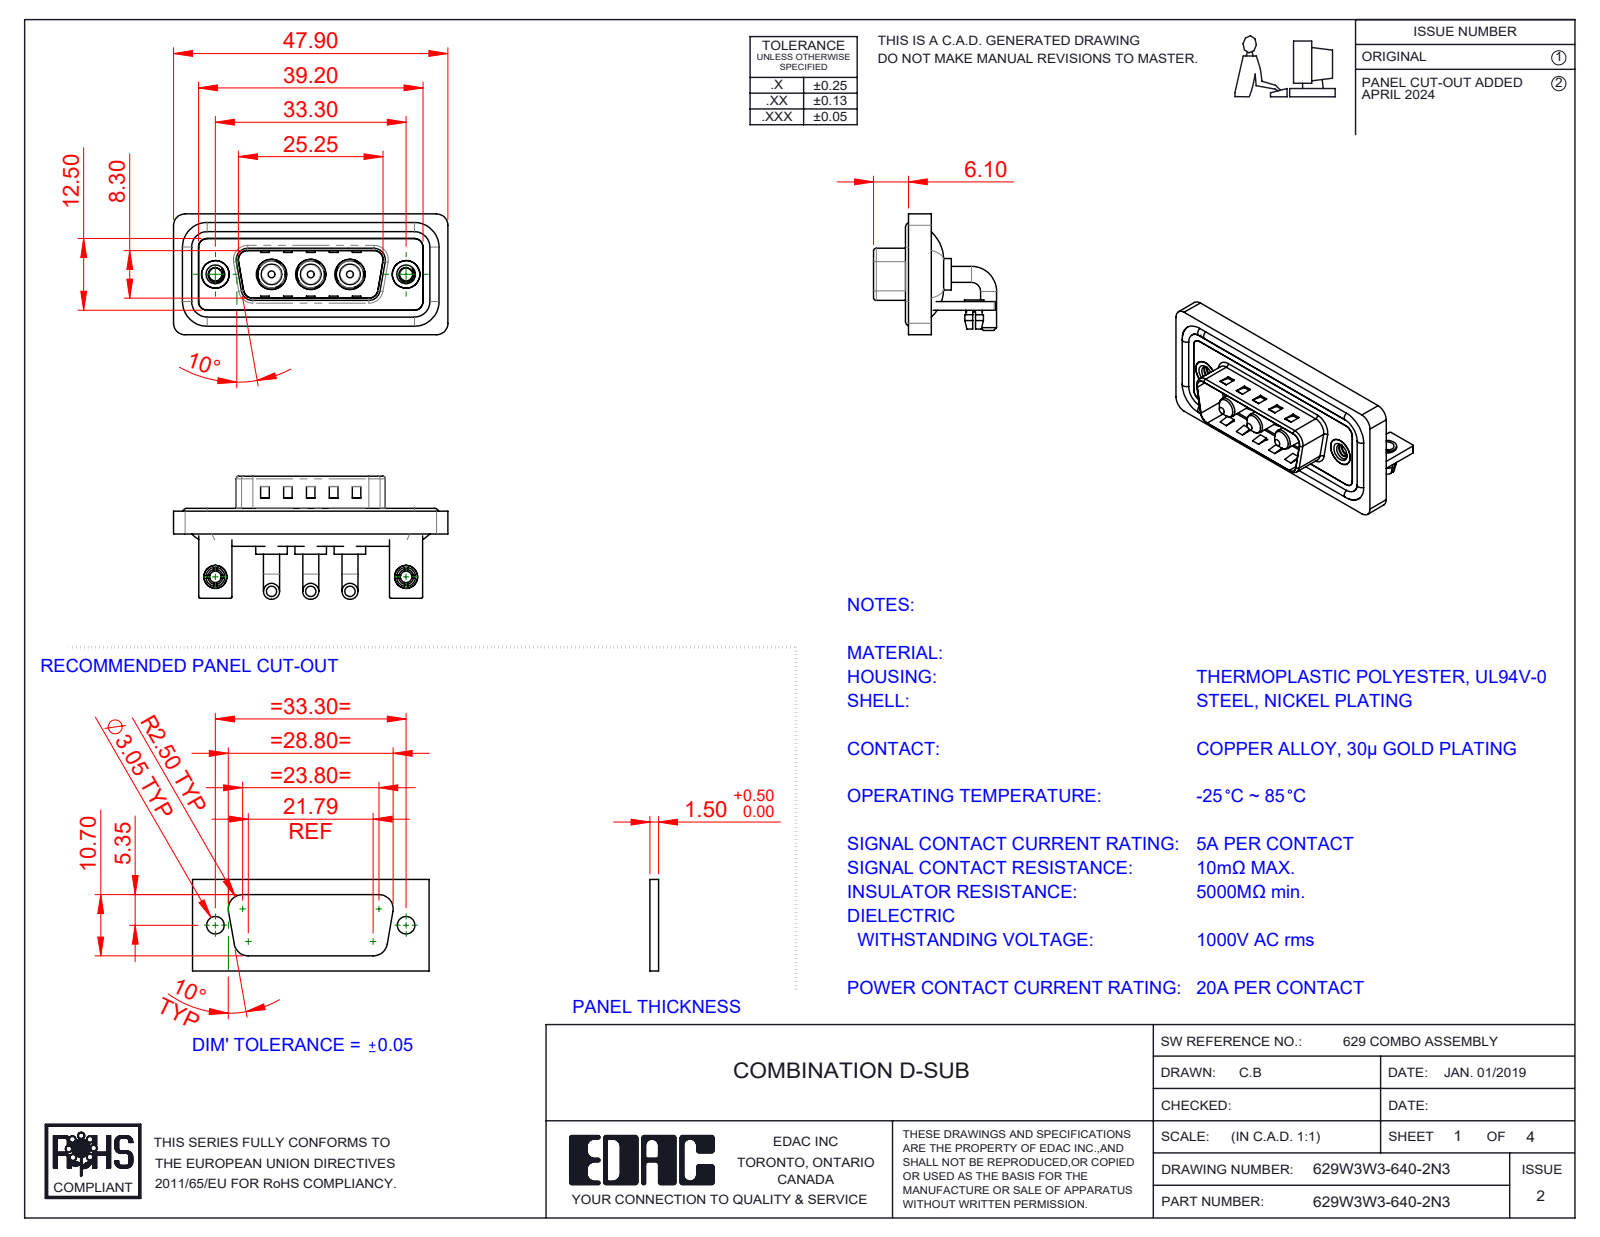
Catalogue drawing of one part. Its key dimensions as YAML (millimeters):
part_name: "629Combo Stabilizer Bracket; 629Combo Board Lock; 629Combo Shell Front_15 Contacts; 629W3W3-640-2N3 (+5 more)"
step_written_by: "SolidWorks 2023 (CONFIG_CONTROL_DESIGN)"
units: millimeters
bodies: {solids: 17, faces: 708, planar: 275, cylindrical: 297, other: 136}
overall_size: [47.9, 21.5, 21.1]
volume: 6092
surface_area: 9833
round_holes:
  - {diameter: 4.85, count: 3}
  - {diameter: 5.3, count: 3}
  - {diameter: 2, count: 2}
  - {diameter: 2.26, count: 2}
  - {diameter: 2.5, count: 2}
  - {diameter: 3.2, count: 2}
  - {diameter: 4, count: 2}
  - {diameter: 4.8, count: 2}
  - {diameter: 5, count: 2}
round_bosses_or_shafts:
  - {diameter: 2.8, count: 6}
  - {diameter: 1.6, count: 4}
  - {diameter: 5.5, count: 3}
  - {diameter: 5.2, count: 3}
  - {diameter: 4.75, count: 3}
  - {diameter: 3.75, count: 3}
  - {diameter: 3.6, count: 3}
  - {diameter: 4.9, count: 2}
partial_cylinders:
  - {radius: 2, count: 21}
  - {radius: 1.5, count: 18}
  - {radius: 0.25, count: 16}
  - {radius: 0.5, count: 9}
  - {radius: 1.6, count: 8}
  - {radius: 0.6, count: 4}
  - {radius: 0.65, count: 4}
  - {radius: 0.9, count: 4}
face_to_face_distances: [0.4, 1.5, 0.8, 2.9, 1.1, 2.1, 3.7, 1.6, 1.2, 4.5]
hole_center_spacings: [6.85, 9.8, 16.65, 23.5, 33.3, 13.7]
